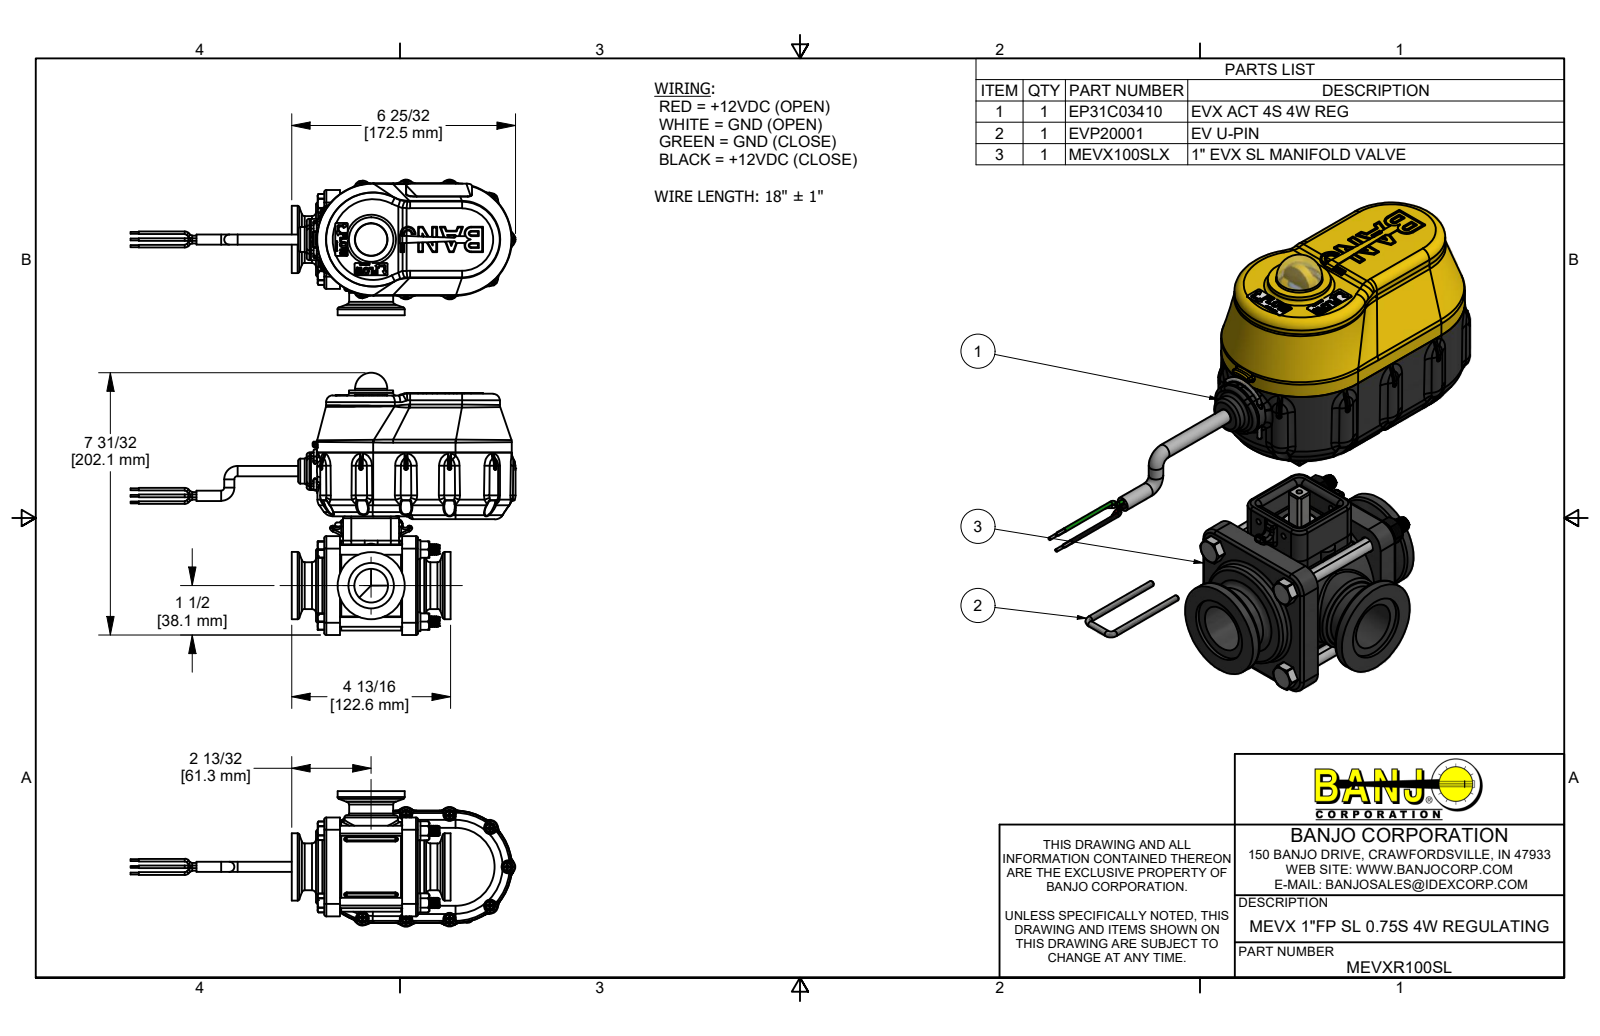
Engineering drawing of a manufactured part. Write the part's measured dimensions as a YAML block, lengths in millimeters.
part_name: "MEVXR100SL; MEVX100SLX; MEVX10354AS; MEVX10354ASX (+8 more)"
step_written_by: "Autodesk Inventor 2019 (AUTOMOTIVE_DESIGN)"
units: millimeters
bodies: {solids: 97, faces: 13181, planar: 3878, cylindrical: 3461, other: 5842}
overall_size: [296.8, 202.1, 104.5]
volume: 876900
surface_area: 382800
round_holes:
  - {diameter: 3.8, count: 13}
  - {diameter: 2.4, count: 11}
  - {diameter: 2.7, count: 4}
  - {diameter: 3.2, count: 4}
  - {diameter: 3.4, count: 4}
  - {diameter: 3.5, count: 4}
  - {diameter: 4.3, count: 4}
  - {diameter: 6.4, count: 4}
  - {diameter: 8.2, count: 4}
  - {diameter: 8.9, count: 4}
  - {diameter: 25.9, count: 3}
  - {diameter: 2.3, count: 2}
round_bosses_or_shafts:
  - {diameter: 6.8, count: 60}
  - {diameter: 2, count: 20}
  - {diameter: 6.4, count: 17}
  - {diameter: 3.6, count: 11}
  - {diameter: 2.7, count: 11}
  - {diameter: 2.2, count: 11}
  - {diameter: 1.5, count: 8}
  - {diameter: 8, count: 5}
partial_cylinders:
  - {radius: 1, count: 147}
  - {radius: 0.5, count: 84}
  - {radius: 0.3, count: 56}
  - {radius: 1.5, count: 46}
  - {radius: 0.1, count: 41}
  - {radius: 0.8, count: 32}
  - {radius: 2, count: 28}
  - {radius: 2.5, count: 22}
face_to_face_distances: [2.5, 65.2, 12.2, 1.4, 60.1, 3.2, 42.8, 1.1, 19.8, 62.6]
hole_center_spacings: [39.3, 42.2, 48, 55.6, 83.7, 69.3, 77.1, 87.6]
